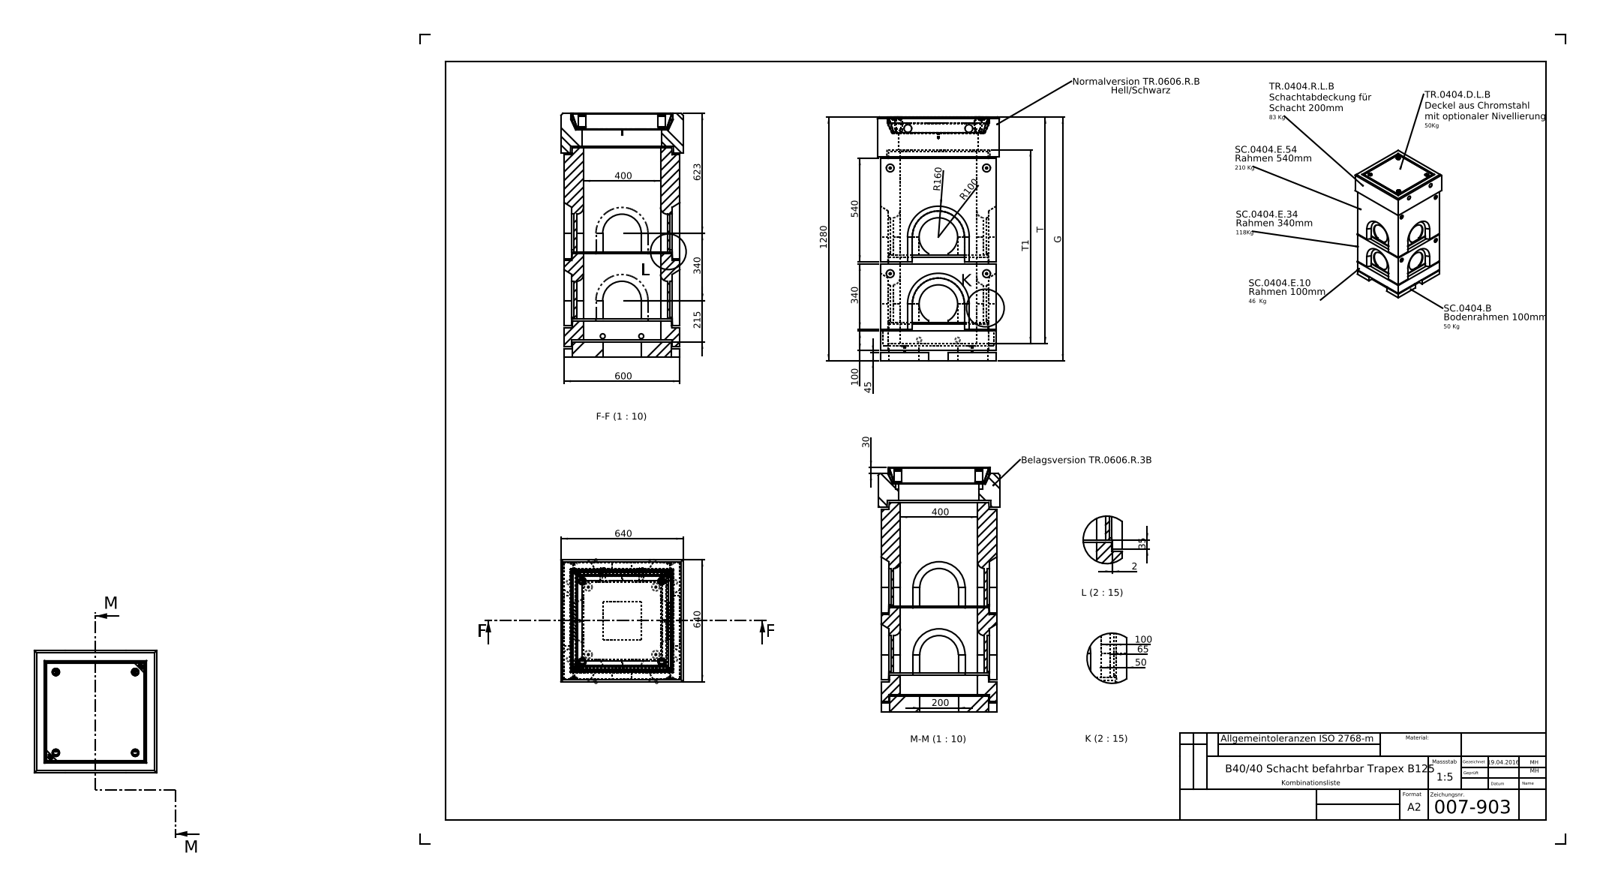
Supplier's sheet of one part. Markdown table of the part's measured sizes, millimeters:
| quantity | value |
| --- | --- |
| part name | SC-TR.0404.120.ef |
| STEP written by | SolidWorks 2018 (AUTOMOTIVE_DESIGN) |
| units | millimeters |
| bodies | 0 solids, 329 faces (218 planar, 68 cylindrical, 43 other) |
| overall size | 1266.16 × 633 × 633 |
| round holes (diameter × count) | 40 × 5, 26.5 × 4, 35 × 4, 200 × 4 |
| round bosses / shafts (diameter × count) | 10 × 6, 5.81 × 6, 32 × 1 |
| partial cylindrical surfaces (radius × count) | 35 × 8, 2.5 × 4, 13.5 × 4 |
| main face-to-face distances | 600, 100, 500, 50, 16.5, 616.5, 116.5, 516.5, 10, 35 |
| hole center spacings | 295.74, 314.01, 348, 411.7, 419, 436.65, 500, 548 |
